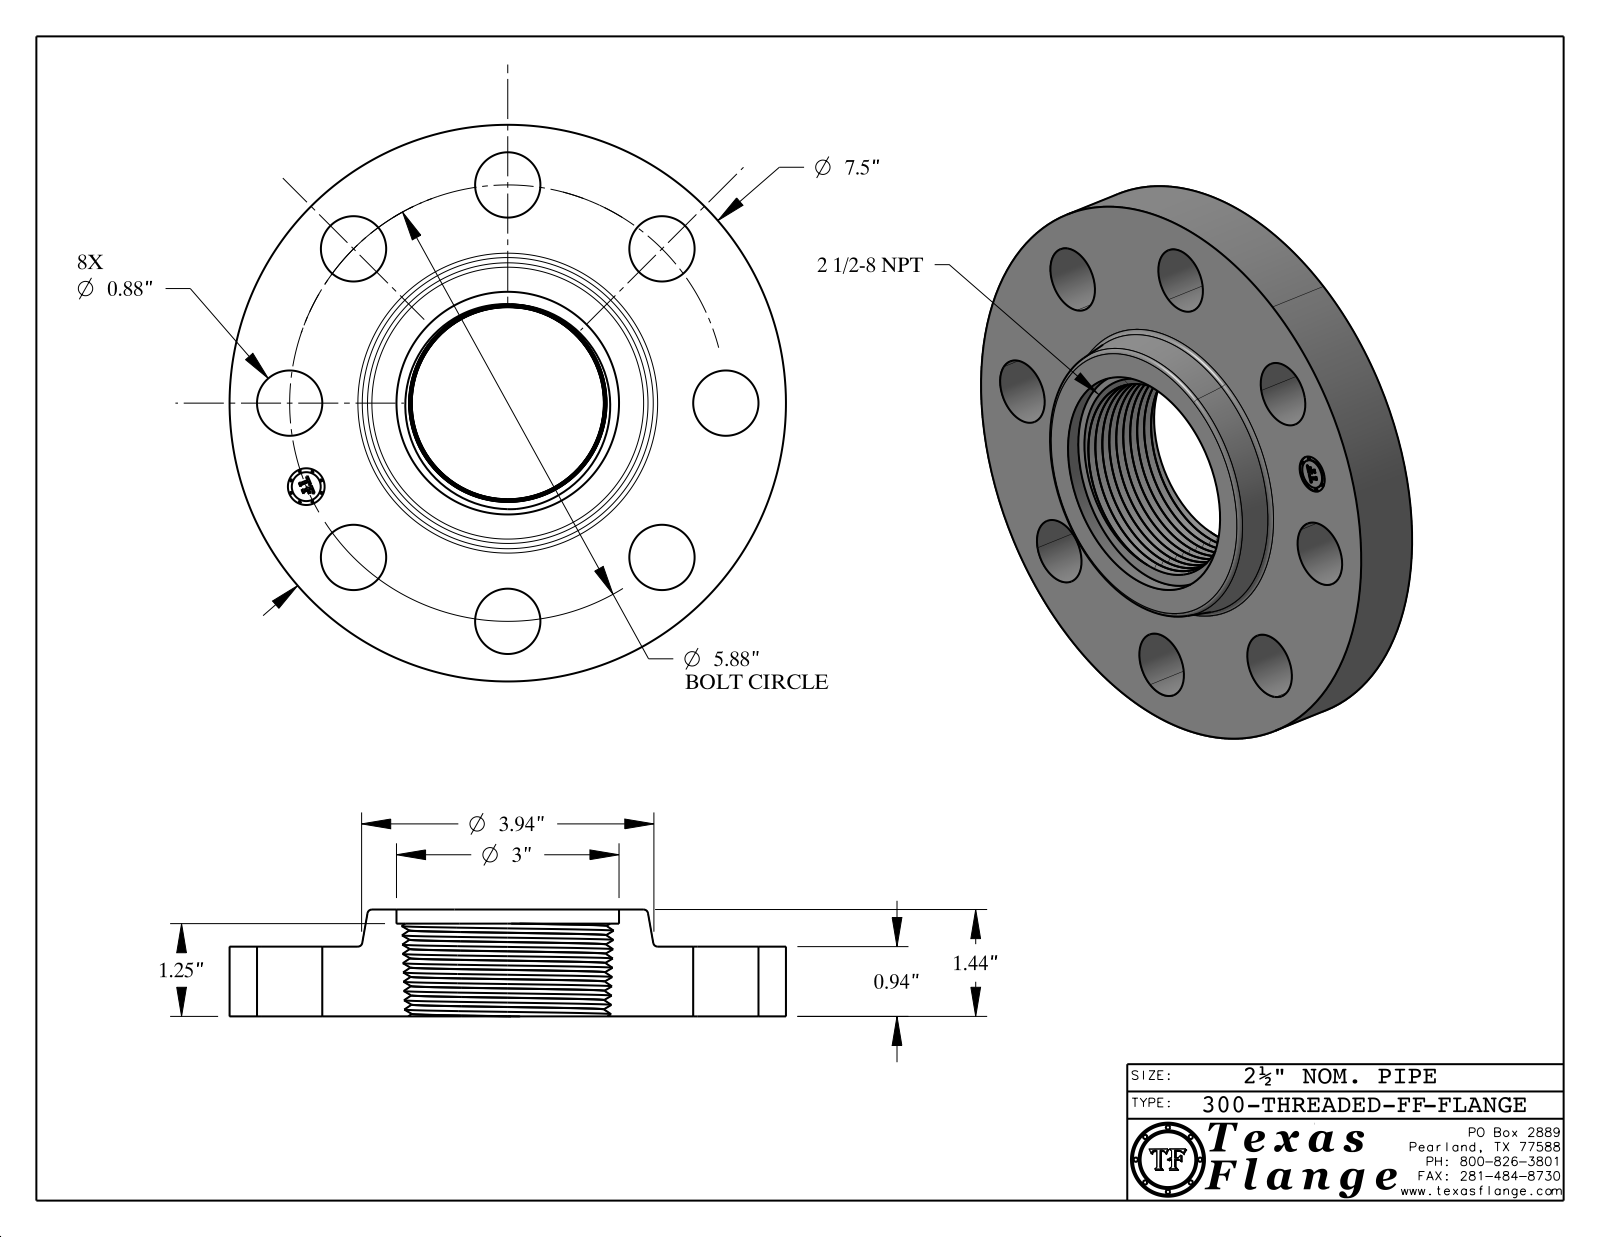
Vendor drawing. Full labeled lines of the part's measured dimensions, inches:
Part name (STEP PRODUCT): 300-THREADED-FF
STEP written by: CATIA V5 STEP AP214 (AUTOMOTIVE_DESIGN)
Units: inches
Bodies: 1 solid, 522 faces (369 planar, 40 cylindrical, 113 other)
Overall size (bounding box): 7.5 × 7.5 × 1.44
Volume: 34.15 in³ · Surface area: 136.5 in²
Round holes (diameter × count): ⌀0.88 ×8, ⌀0.495 ×1, ⌀3 ×1
Round bosses / shafts (diameter × count): ⌀0.03 ×8, ⌀7.5 ×1, ⌀0.39 ×1
Main face-to-face distances: 0.94, 1.44, 0.5, 1.25, 0.31, 0.19, 0.015, 0.925, 0.325, 0.515
Hole centre spacings: 2.25, 5.432, 2.94, 2.94, 4.157, 4.158, 3.267, 5.88
